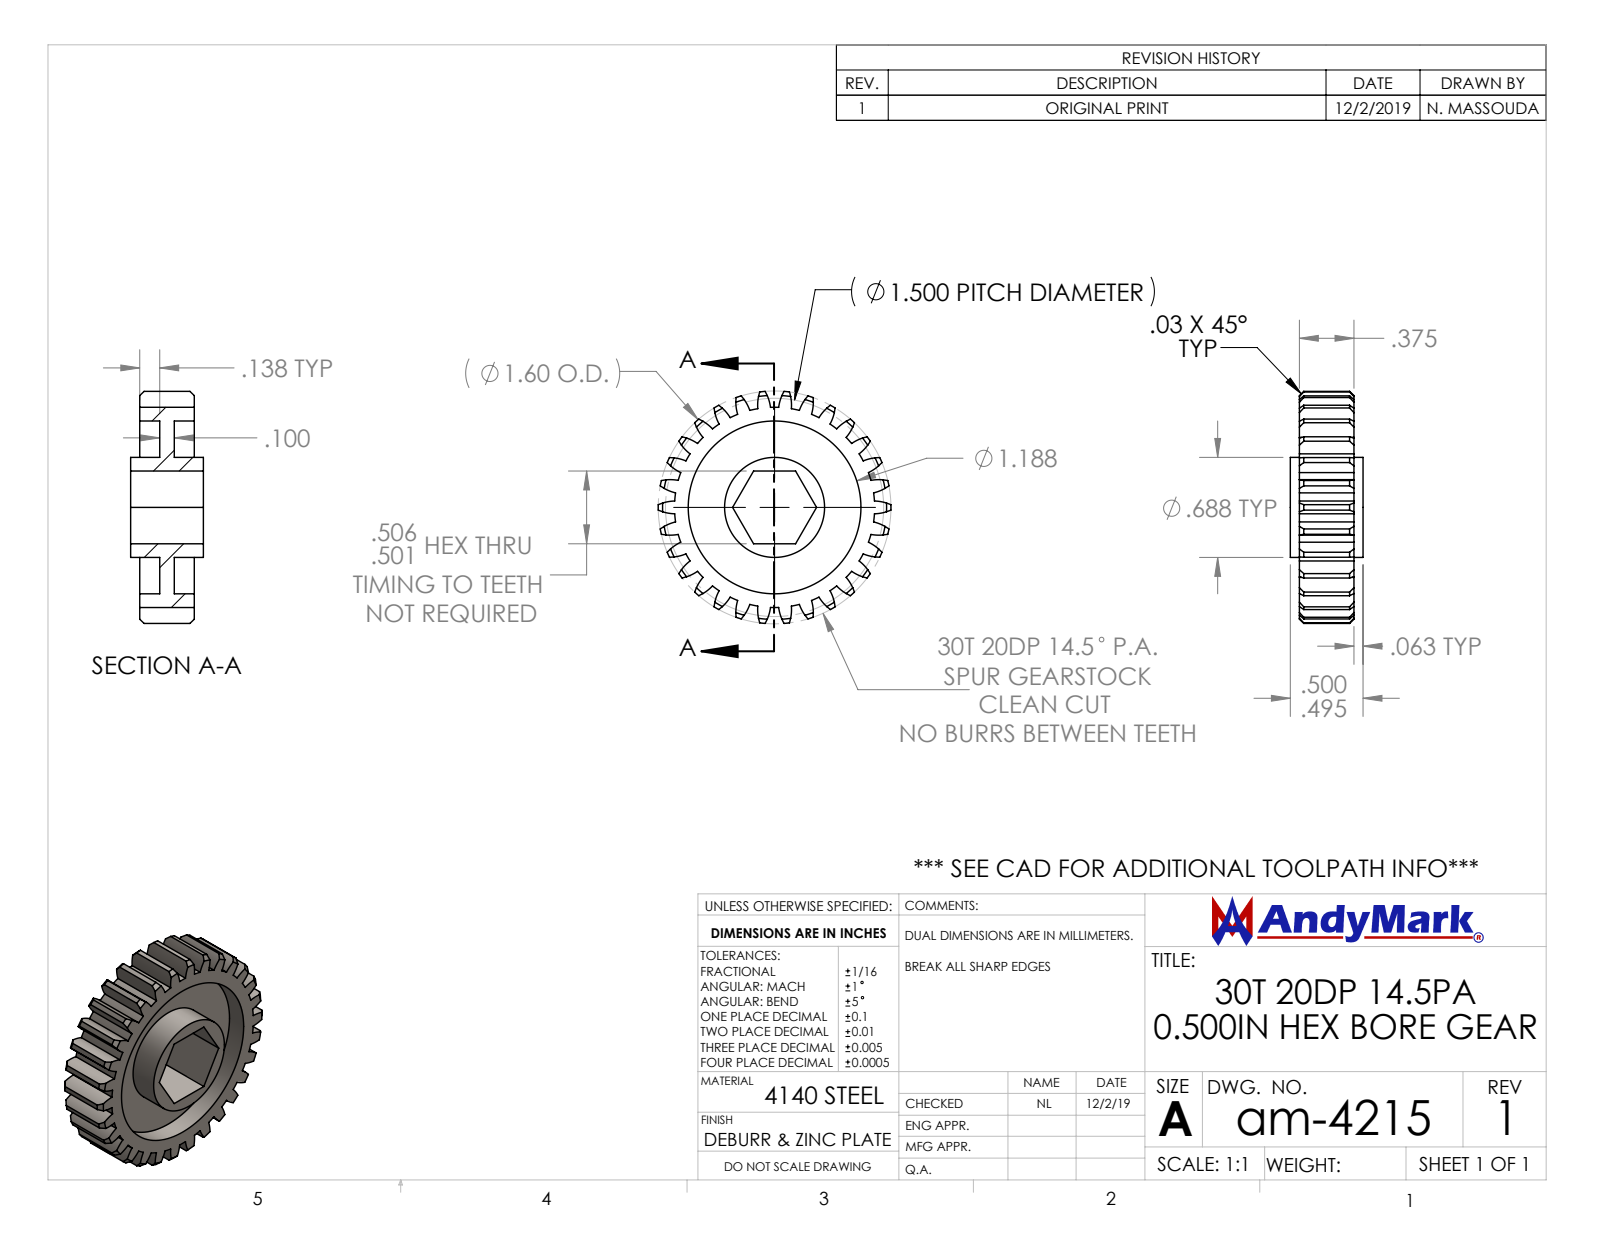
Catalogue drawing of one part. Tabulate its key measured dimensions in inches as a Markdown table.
| quantity | value |
| --- | --- |
| part name | am-4215 30T 20DP 500hex 375 FW |
| STEP written by | SolidWorks 2019 (CONFIG_CONTROL_DESIGN) |
| units | inches |
| bodies | 1 solid, 205 faces (12 planar, 133 cylindrical, 60 other) |
| overall size | 1.6 × 1.595 × 0.5 |
| volume | 0.381 in³ |
| surface area | 9.362 in² |
| round holes (diameter × count) | 1.187 × 1 |
| round bosses / shafts (diameter × count) | 0.687 × 1 |
| partial cylindrical surfaces (radius × count) | 0.3 × 60, 0.688 × 1, 0.8 × 1 |
| main face-to-face distances | 0.1, 0.5, 0.137, 0.237, 0.375, 0.238, 0.138, 0.2, 0.3, 0.063 |
